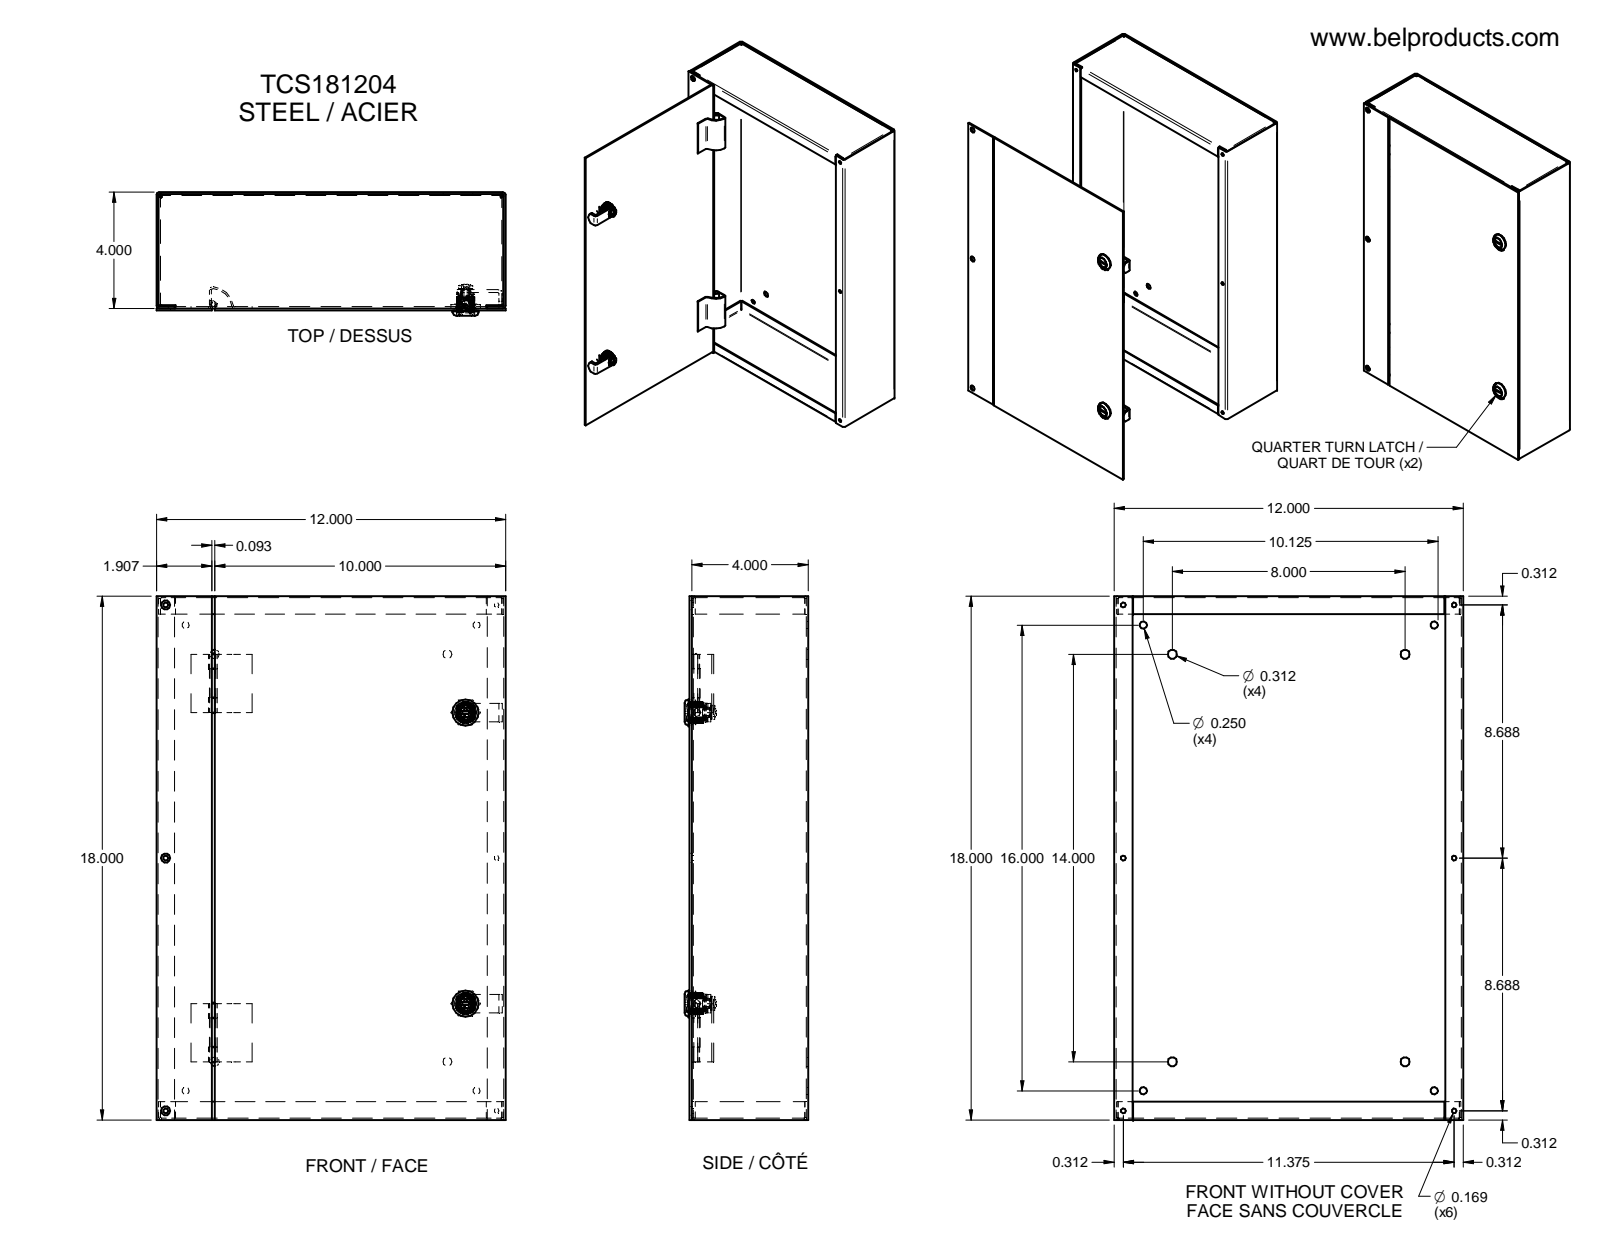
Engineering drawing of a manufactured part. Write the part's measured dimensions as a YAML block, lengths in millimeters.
part_name: "LOCK AVEC TOURNEVIS TYPE 4-12 SANS CAME; HOSING-oa0; INSERT POUR TOURNEVIS-oa1; NOIX DE FIXATION-oa2 (+8 more)"
step_written_by: "Unknown (AUTOMOTIVE_DESIGN)"
units: millimeters
bodies: {solids: 27, faces: 1077, planar: 536, cylindrical: 261, other: 280}
overall_size: [457.2, 304.8, 107.97]
volume: 785346
surface_area: 970429
round_holes:
  - {diameter: 7.92, count: 7}
  - {diameter: 4.29, count: 6}
  - {diameter: 6.35, count: 4}
  - {diameter: 6.99, count: 2}
  - {diameter: 9.1, count: 2}
  - {diameter: 11.18, count: 2}
  - {diameter: 12.83, count: 2}
  - {diameter: 15.8, count: 2}
  - {diameter: 17.46, count: 2}
  - {diameter: 3.81, count: 1}
round_bosses_or_shafts:
  - {diameter: 22.86, count: 2}
  - {diameter: 22.61, count: 2}
  - {diameter: 15.75, count: 2}
  - {diameter: 12.95, count: 2}
  - {diameter: 12.62, count: 2}
  - {diameter: 12.19, count: 2}
  - {diameter: 11.86, count: 2}
  - {diameter: 10.08, count: 2}
partial_cylinders:
  - {radius: 9.53, count: 22}
  - {radius: 0.25, count: 16}
  - {radius: 0.81, count: 13}
  - {radius: 2.34, count: 12}
  - {radius: 9.42, count: 4}
  - {radius: 1.52, count: 2}
  - {radius: 3.05, count: 2}
  - {radius: 6.22, count: 2}
face_to_face_distances: [1.52, 100.08, 101.6, 1.91, 101.99, 103.51, 303.28, 455.68, 304.8, 301.76]
hole_center_spacings: [24.69, 35.92, 60.61, 182.89, 203.95, 220.66, 230.01, 249.76]
